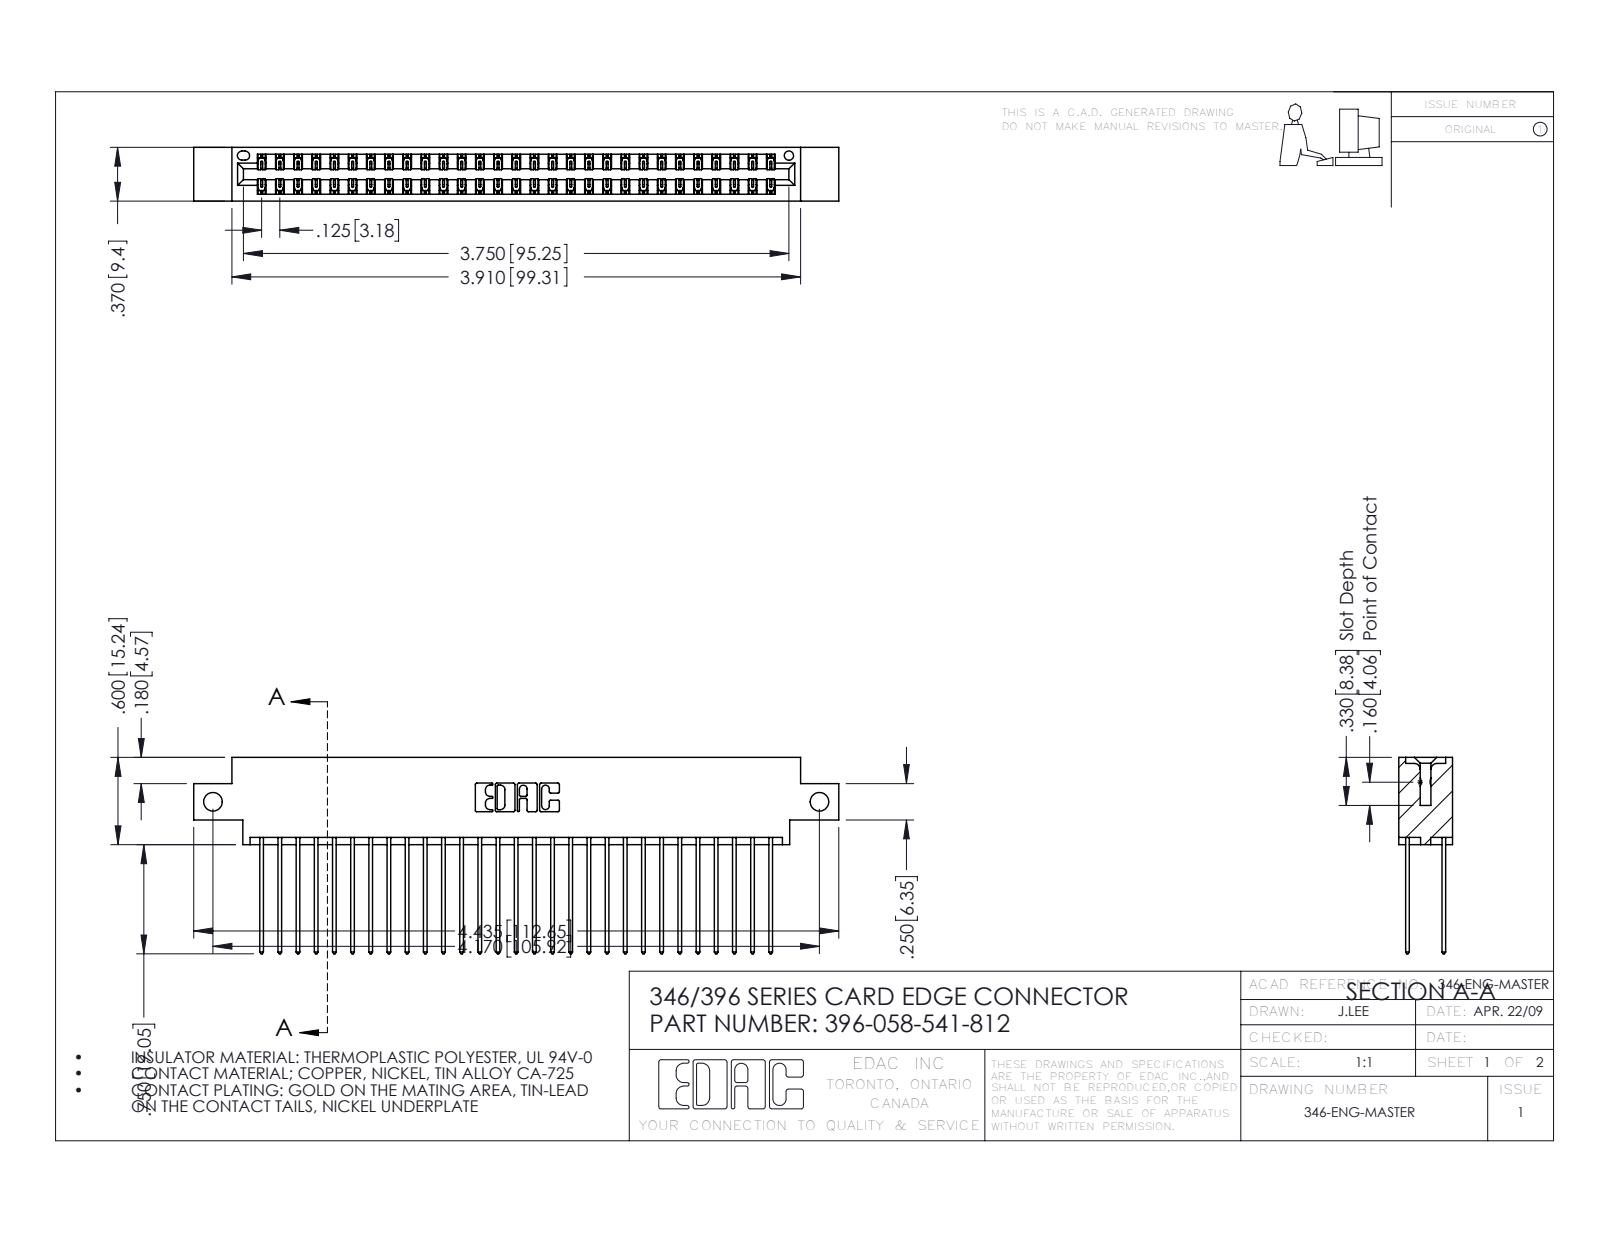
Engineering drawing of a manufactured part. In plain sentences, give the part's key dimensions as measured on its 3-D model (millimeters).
The part is named "396-058-541-812; 345-292-001_345-293-141; 346 Part_0.170 Offset - Side Mount". Its 3-D file was written by "SolidWorks 2016 (CONFIG_CONTROL_DESIGN)". It is 59 solids with 3142 faces: 2110 planar, 1032 cylindrical and 0 other. Overall it measures 112.6 by 34.3 by 9.4 millimeters. Its volume is 11 000 cubic millimeters and its surface area 16 520 square millimeters. Round holes: 2 of diameter 3.3, 1 of diameter 1.6. Partial cylindrical surfaces (rounded edges, fillets, slot ends): 87 of radius 0.2, 58 of radius 0.3, 22 of radius 0.3, 6 of radius 0.2, 6 of radius 0.8, 3 of radius 0.7, 2 of radius 0.4, 2 of radius 0.6. The main face-to-face distances are 1.2, 8.2, 6.4, 1.8, 7.6, 0.6, 9.4, 7, 5.7, 3.8. The hole center spacings are 105.9.
